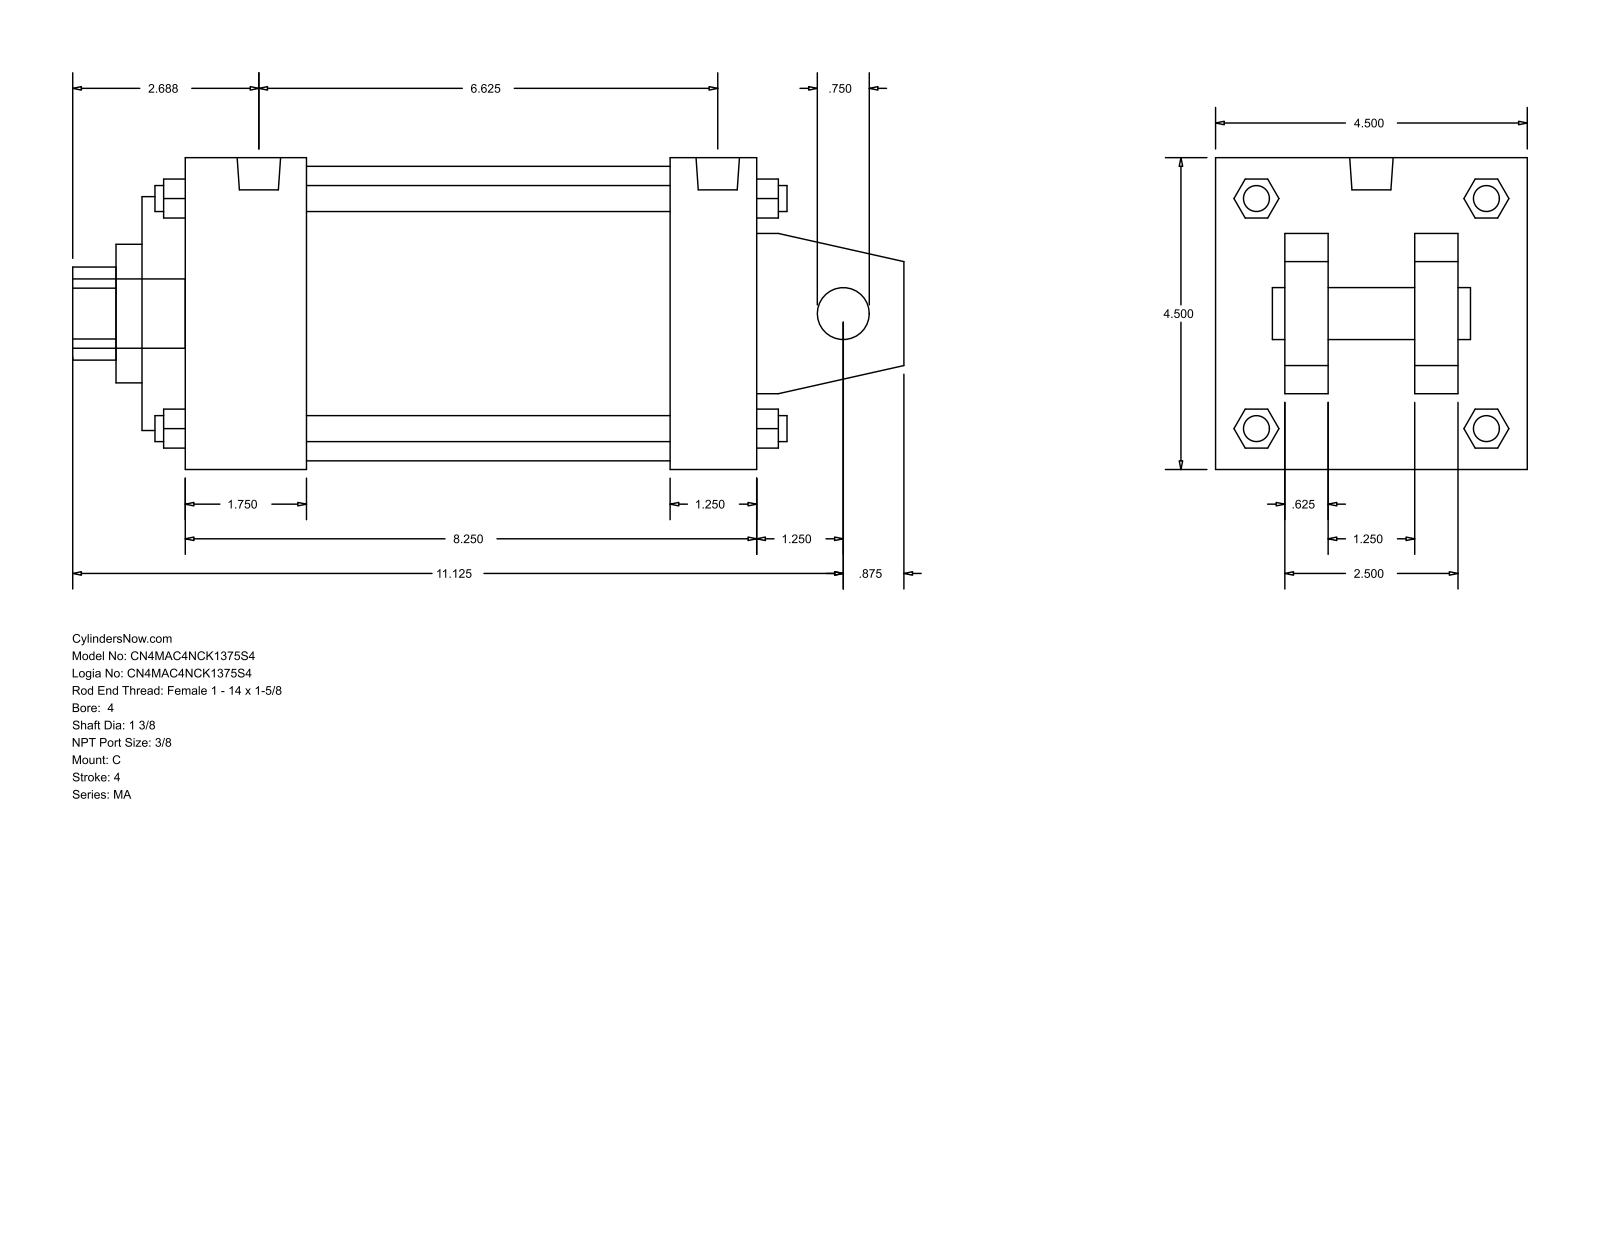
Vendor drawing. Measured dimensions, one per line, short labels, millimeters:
name: MA_C__0400_1.375
written by: GSSL Pune (CONFIG_CONTROL_DESIGN)
unit: mm
bodies: 0 solids, 141 faces (109 planar, 32 cylindrical, 0 other)
size: 304.8 × 114.3 × 114.3
holes: 1× ⌀19.05, 1× ⌀34.92, 1× ⌀50.8, 1× ⌀85.72, 1× ⌀107.95
bosses: 4× ⌀11.11, 4× ⌀9.53, 2× ⌀15.93, 1× ⌀25.4
rounds: 1× R17.06
face distances: 114.3, 15.87, 209.55, 73.03, 41.27, 25.4, 88.9, 47.63, 225.42, 193.67
